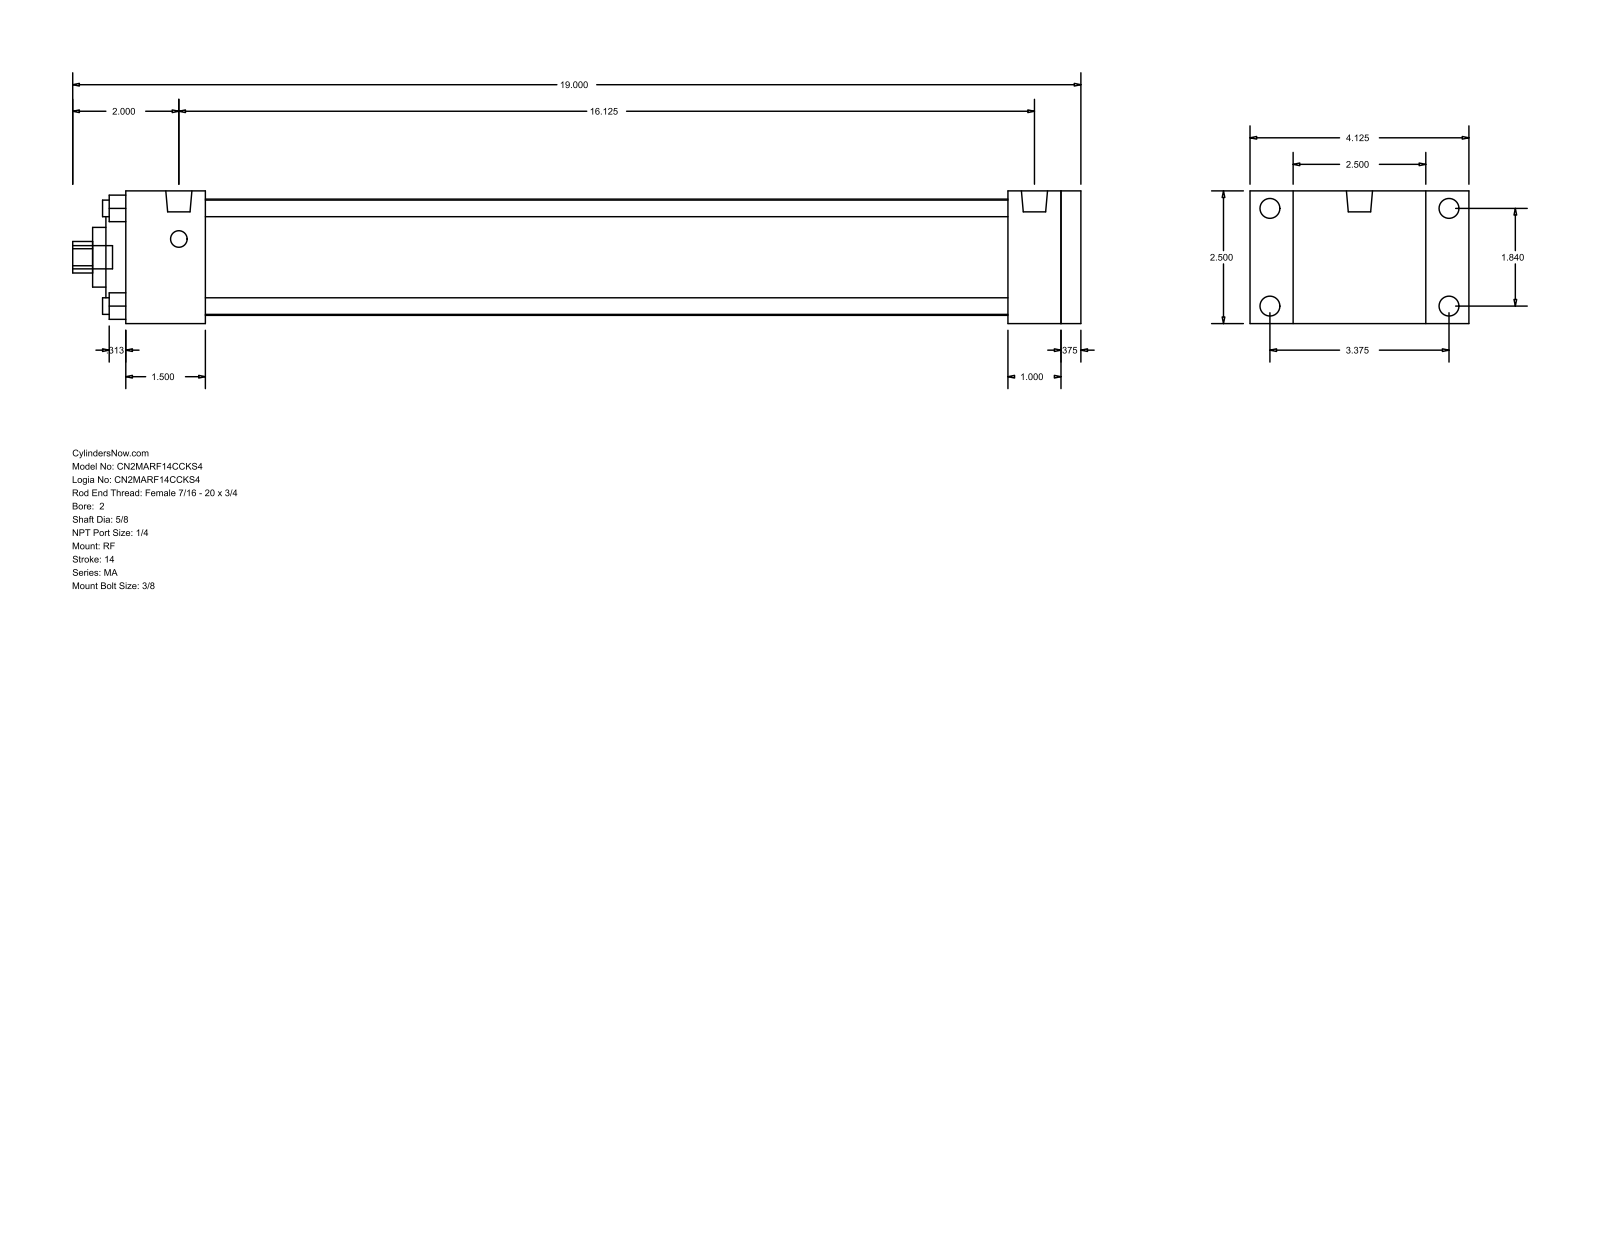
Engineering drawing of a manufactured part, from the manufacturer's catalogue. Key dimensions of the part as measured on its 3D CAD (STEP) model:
Part name (STEP PRODUCT): MA_RF__0200_0.625
STEP written by: GSSL Pune (CONFIG_CONTROL_DESIGN)
Units: millimetres
Bodies: 0 solids, 94 faces (65 planar, 29 cylindrical, 0 other)
Overall size (bounding box): 482.6 × 104.78 × 63.5
Round holes (diameter × count): ⌀7.94 ×4, ⌀15.88 ×1, ⌀28.57 ×1, ⌀50.8 ×1, ⌀55.63 ×1
Round bosses / shafts (diameter × count): ⌀9.53 ×4, ⌀7.94 ×4, ⌀12.49 ×2, ⌀11.11 ×1
Partial cylindrical surfaces — rounded edges, fillets, slot ends (radius × count): R7.54 ×1
Main face-to-face distances: 63.5, 9.53, 38.1, 9.52, 447.67, 457.2, 466.72, 409.57, 419.1, 422.28
Hole centre spacings: 33.05, 46.74, 66.1
